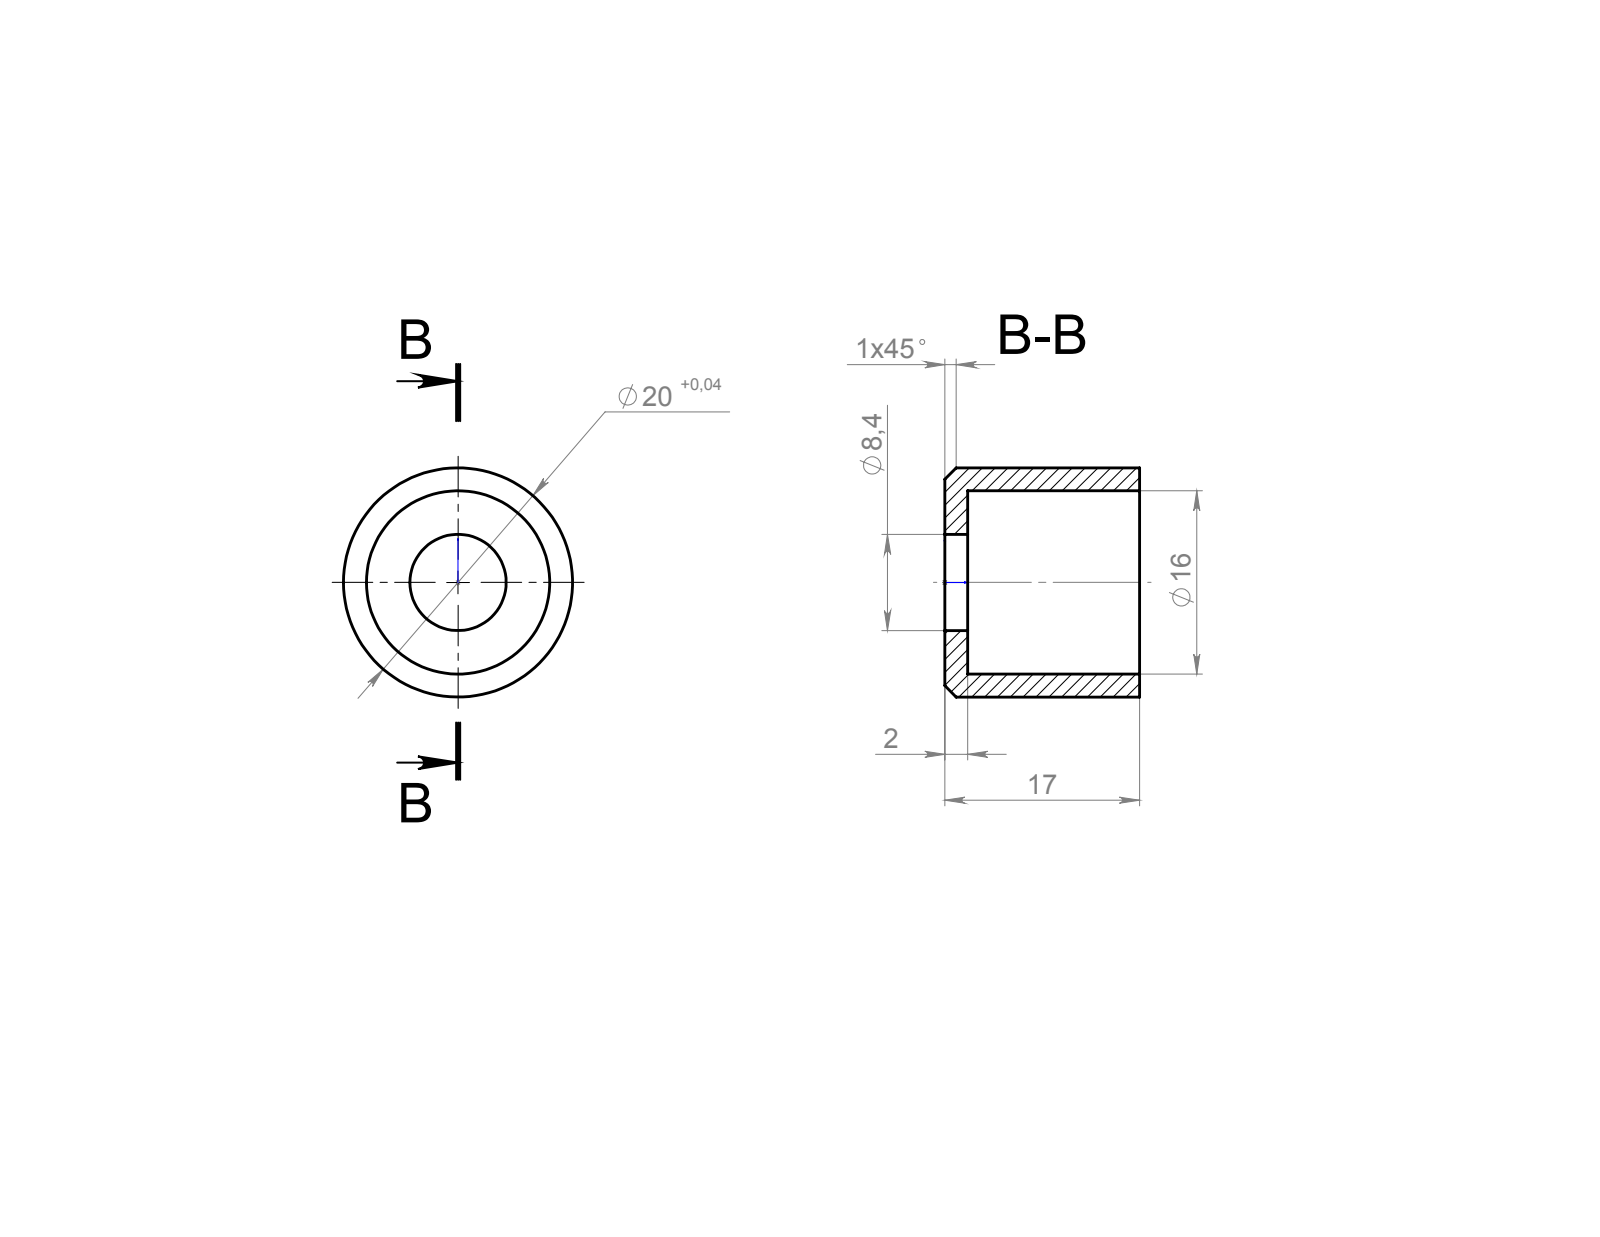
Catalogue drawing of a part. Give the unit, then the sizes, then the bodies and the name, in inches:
Units: inches
Overall size (bounding box): 2.244 × 2.244 × 1.654
Round holes (diameter × count): ⌀1.693 ×1, ⌀2.008 ×1
Round bosses / shafts (diameter × count): ⌀2.244 ×1, ⌀1.929 ×1
Main face-to-face distances: 0.079, 1.654, 1.575
Volume: 1.43 in³ · Surface area: 27.52 in²
Bodies: 1 solid, 10 faces (3 planar, 4 cylindrical, 3 other)
Part name (STEP PRODUCT): Стакан
STEP written by: ASCON Math Kernel (AUTOMOTIVE_DESIGN)
